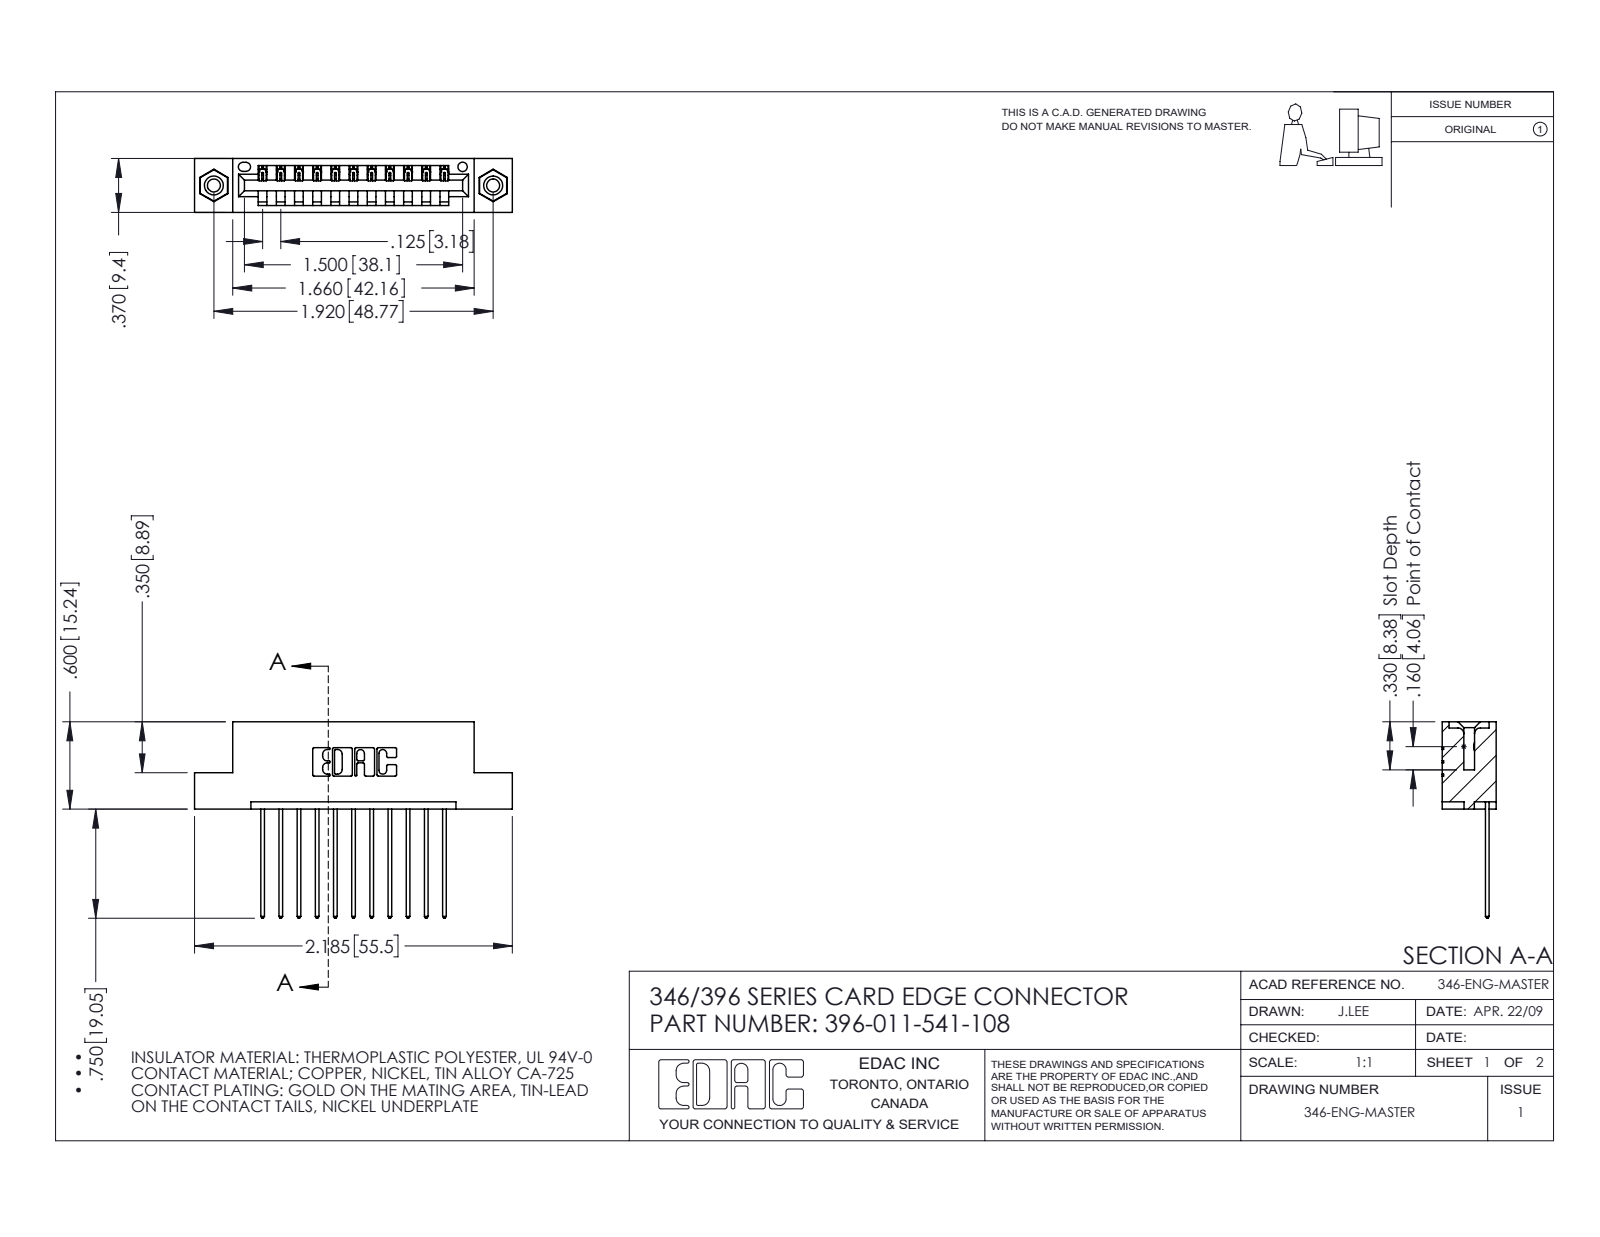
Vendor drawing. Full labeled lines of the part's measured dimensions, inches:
Part name (STEP PRODUCT): 345-292-001_345-293-141; 346 Part_Flush Mounting Lugs - 0.156 Dia-TI; 396-011-541-108; 345-250-001_345-250-003-102
STEP written by: SolidWorks 2016 (CONFIG_CONTROL_DESIGN)
Units: inches
Bodies: 14 solids, 820 faces (548 planar, 256 cylindrical, 16 other)
Overall size (bounding box): 2.185 × 1.35 × 0.37
Volume: 0.313 in³ · Surface area: 9.787 in²
Round holes (diameter × count): ⌀0.089 ×2, ⌀0.125 ×2, ⌀0.156 ×2, ⌀0.064 ×1
Round bosses / shafts (diameter × count): ⌀0.155 ×2
Partial cylindrical surfaces — rounded edges, fillets, slot ends (radius × count): R0.006 ×22, R0.01 ×22, R0.01 ×22, R0.007 ×6, R0.031 ×6, R0.026 ×3, R0.031 ×2, R0.04 ×2
Main face-to-face distances: 0.25, 0.048, 0.322, 0.37, 0.072, 0.298, 0.025, 0.148, 0.222, 0.1
Hole centre spacings: 0.246, 1.715, 1.92
